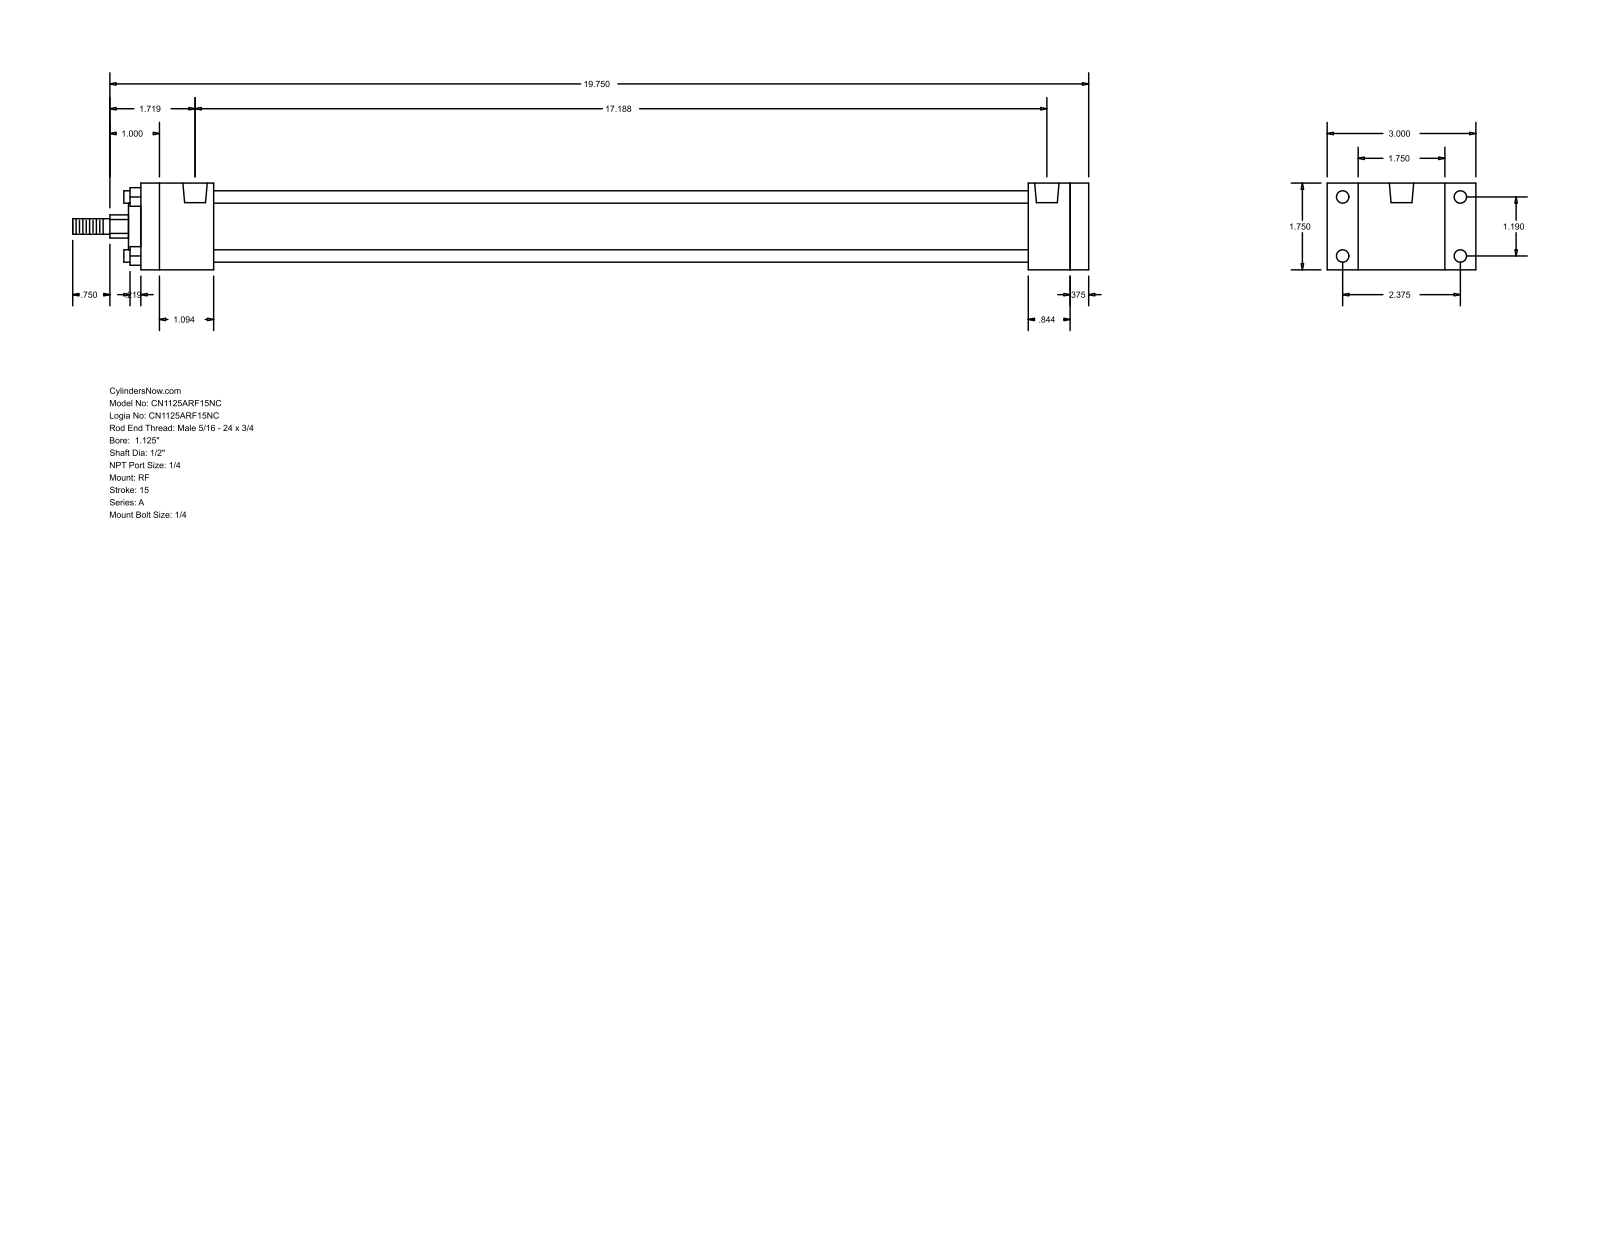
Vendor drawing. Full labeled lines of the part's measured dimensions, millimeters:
Part name (STEP PRODUCT): A_RF__0112_0.5
STEP written by: GSSL Pune (CONFIG_CONTROL_DESIGN)
Units: millimetres
Bodies: 0 solids, 92 faces (64 planar, 28 cylindrical, 0 other)
Overall size (bounding box): 520.7 × 76.2 × 44.45
Round holes (diameter × count): ⌀5.56 ×4, ⌀6.35 ×4, ⌀12.49 ×2
Round bosses / shafts (diameter × count): ⌀6.35 ×4, ⌀31.88 ×1, ⌀23.81 ×1, ⌀12.7 ×1, ⌀7.94 ×1
Partial cylindrical surfaces — rounded edges, fillets, slot ends (radius × count): R5.94 ×1
Main face-to-face distances: 44.46, 9.53, 485.77, 476.24, 37.3, 454.81, 417.51, 438.94, 448.47, 21.43
Hole centre spacings: 30.22, 60.32, 67.47, 433.39, 1.58, 1.59, 434.97, 434.98
